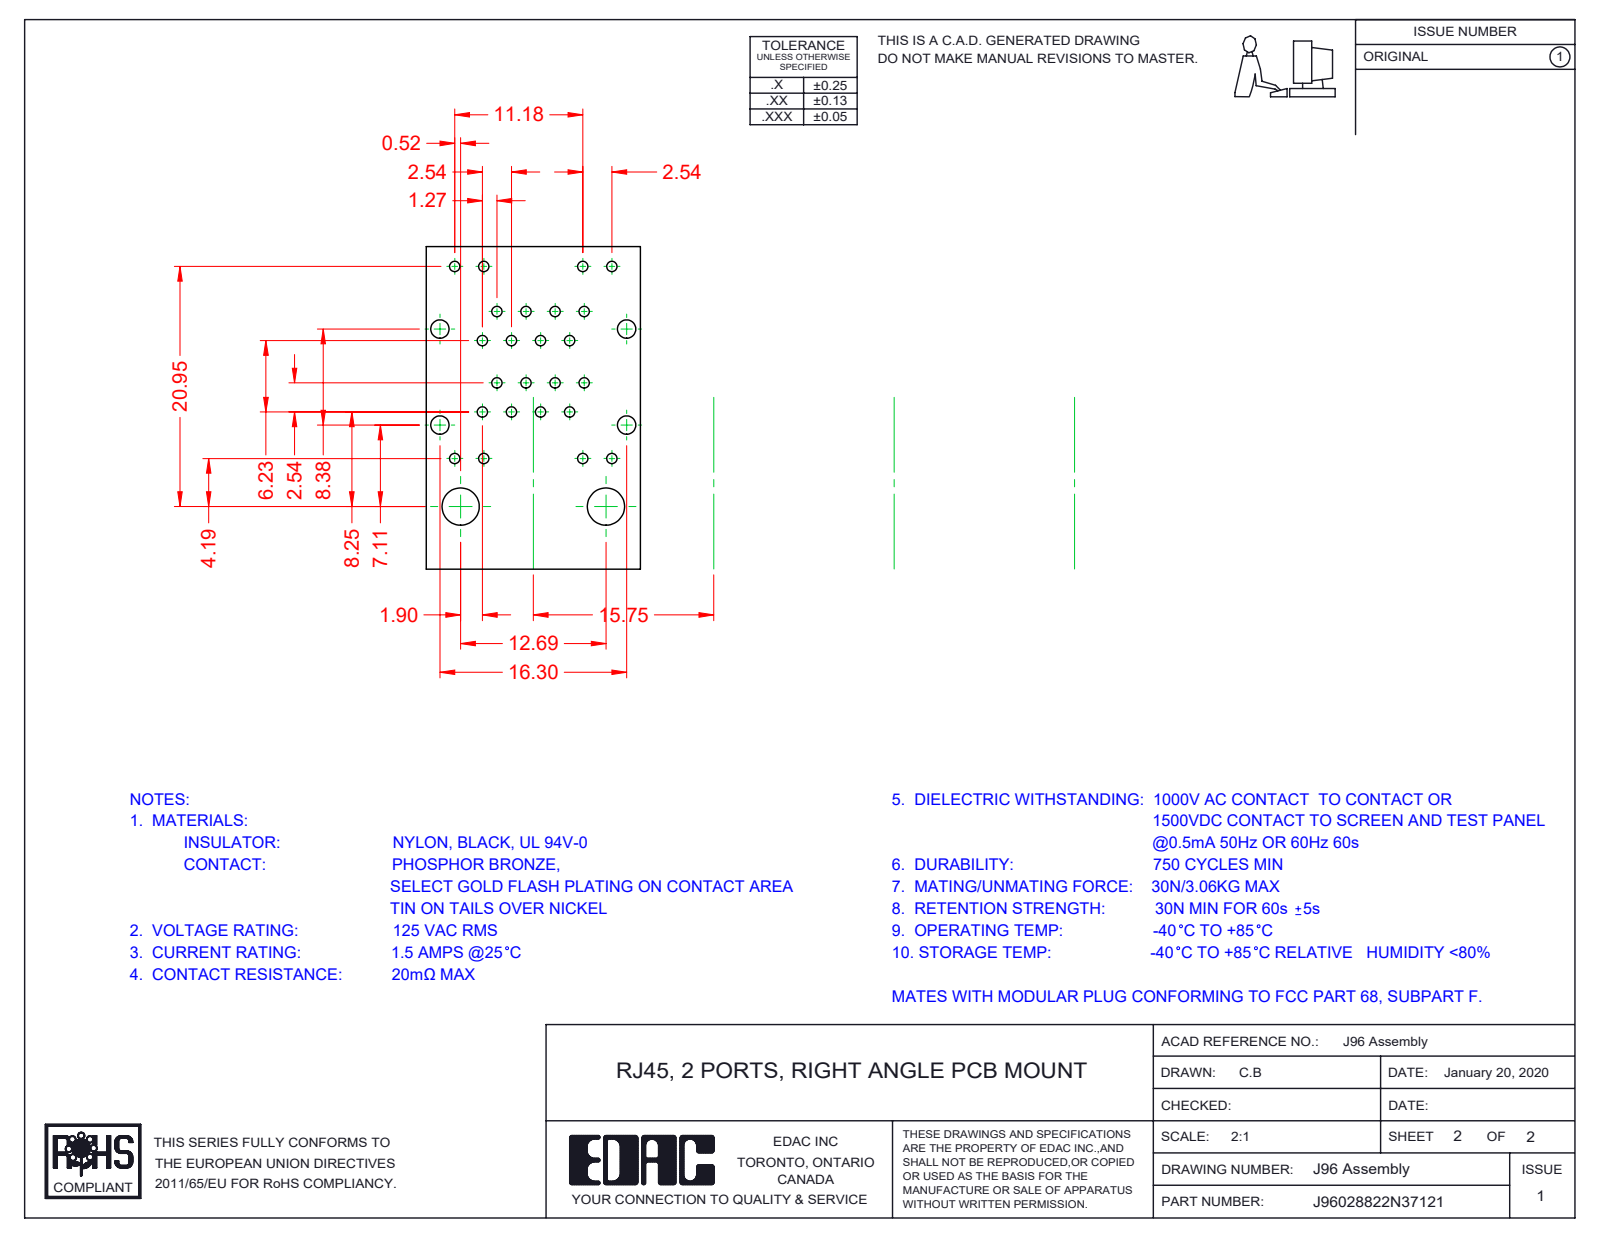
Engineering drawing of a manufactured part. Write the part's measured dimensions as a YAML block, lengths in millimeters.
part_name: "96 LED LH Lower_3-Green; 96 LED LH Upper_3-Green; 96 Insulator Insert; 96 Grounding_2 Ports (+8 more)"
step_written_by: "SolidWorks 2016 (CONFIG_CONTROL_DESIGN)"
units: millimeters
bodies: {solids: 27, faces: 2386, planar: 1849, cylindrical: 431, other: 106}
overall_size: [29.58, 28.68, 16.8]
volume: 6852
surface_area: 19109
partial_cylinders:
  - {radius: 0.25, count: 48}
  - {radius: 0.15, count: 32}
  - {radius: 0.35, count: 24}
  - {radius: 0.5, count: 16}
  - {radius: 1, count: 16}
  - {radius: 0.2, count: 13}
  - {radius: 0.7, count: 9}
  - {radius: 2, count: 5}
face_to_face_distances: [16.3, 16.1, 1.75, 16.5, 14.75, 1.55, 14.55, 0.53, 1.48, 11.2]
